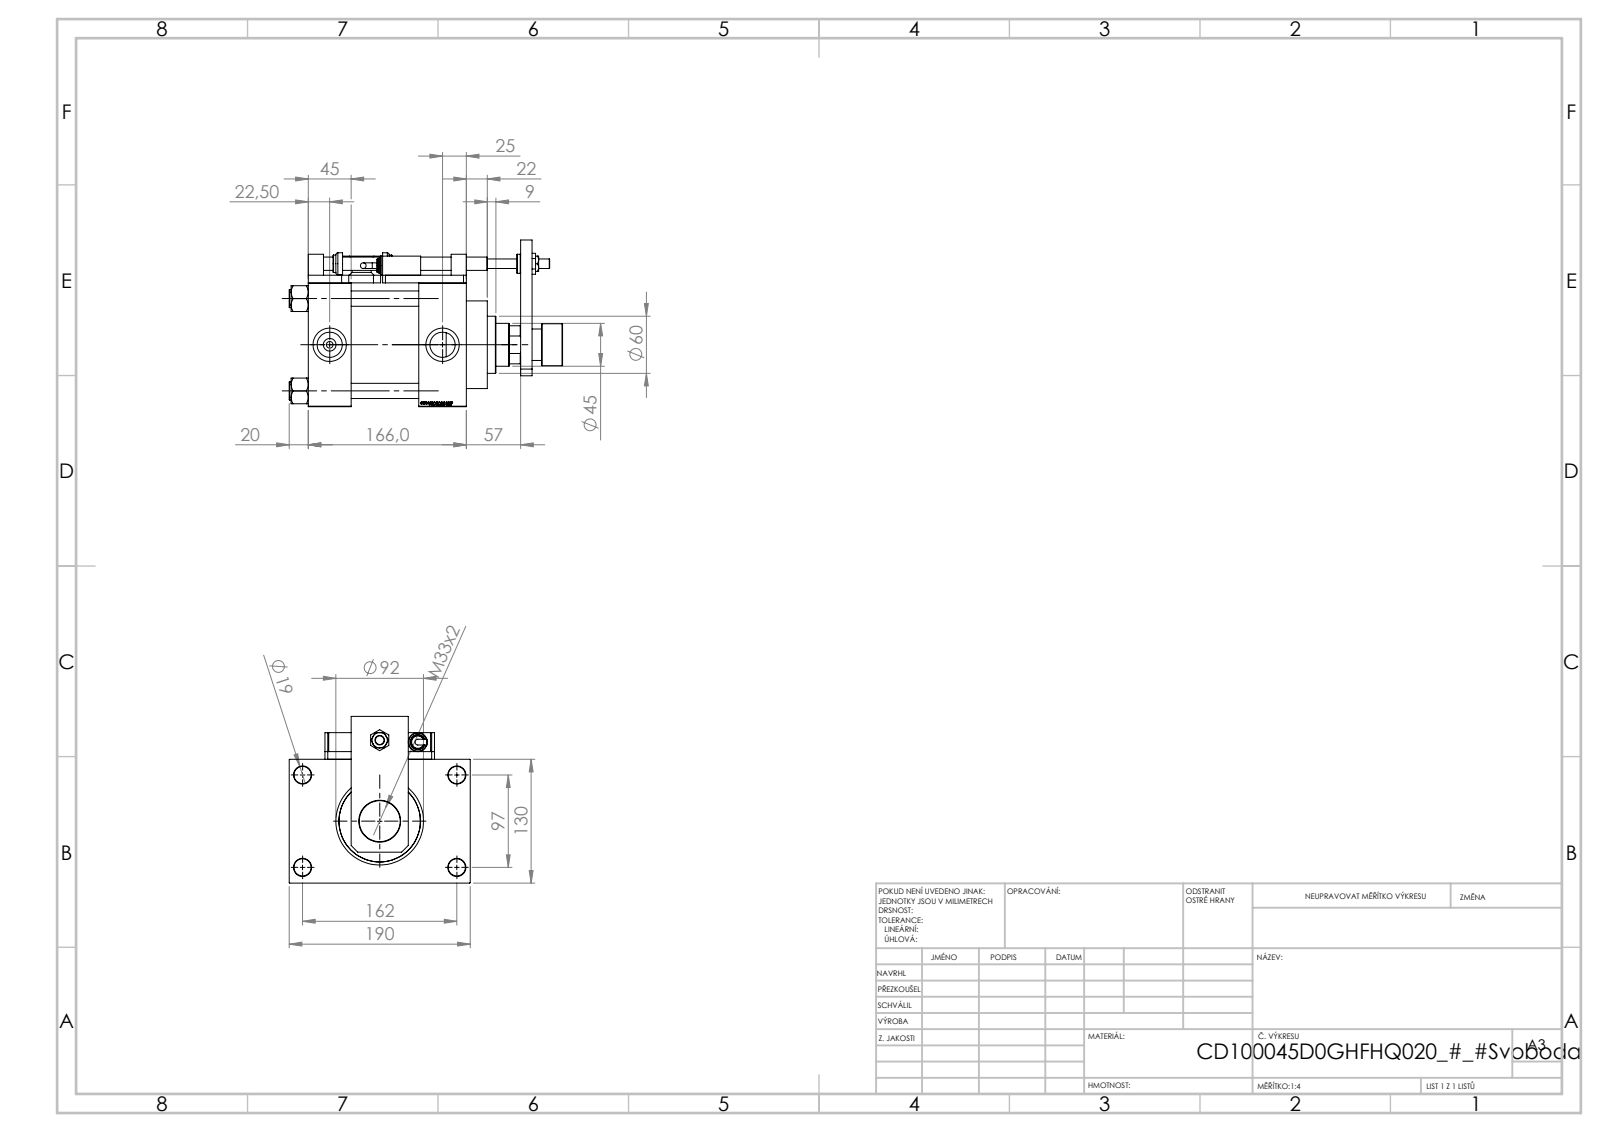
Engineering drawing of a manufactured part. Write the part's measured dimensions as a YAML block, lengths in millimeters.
part_name: "V215CD_D_Body; V215CD_VCP_D; V215CD_SWITCH_Q_PODLOZKA_FRONT; V215CD_SWITCH_Q_NUT10 (+7 more)"
step_written_by: "SolidWorks 2019 (CONFIG_CONTROL_DESIGN)"
units: millimeters
bodies: {solids: 25, faces: 1392, planar: 669, cylindrical: 160, other: 563}
overall_size: [287, 190, 175]
volume: 2972000
surface_area: 460471
round_holes:
  - {diameter: 8.5, count: 4}
  - {diameter: 13.5, count: 4}
  - {diameter: 16, count: 4}
  - {diameter: 18, count: 4}
  - {diameter: 7, count: 2}
  - {diameter: 26.44, count: 2}
  - {diameter: 35, count: 2}
  - {diameter: 10, count: 1}
  - {diameter: 14, count: 1}
  - {diameter: 31.5, count: 1}
  - {diameter: 33, count: 1}
  - {diameter: 45, count: 1}
round_bosses_or_shafts:
  - {diameter: 19, count: 4}
  - {diameter: 20, count: 3}
  - {diameter: 16, count: 2}
  - {diameter: 14, count: 2}
  - {diameter: 6, count: 2}
  - {diameter: 106, count: 1}
  - {diameter: 92, count: 1}
  - {diameter: 60, count: 1}
partial_cylinders:
  - {radius: 7.5, count: 4}
face_to_face_distances: [130, 45, 121, 166, 71, 8, 116, 50, 138, 190]
hole_center_spacings: [32.55, 68.52, 94.41, 96.9, 102.27, 129.45, 161.73, 32]
